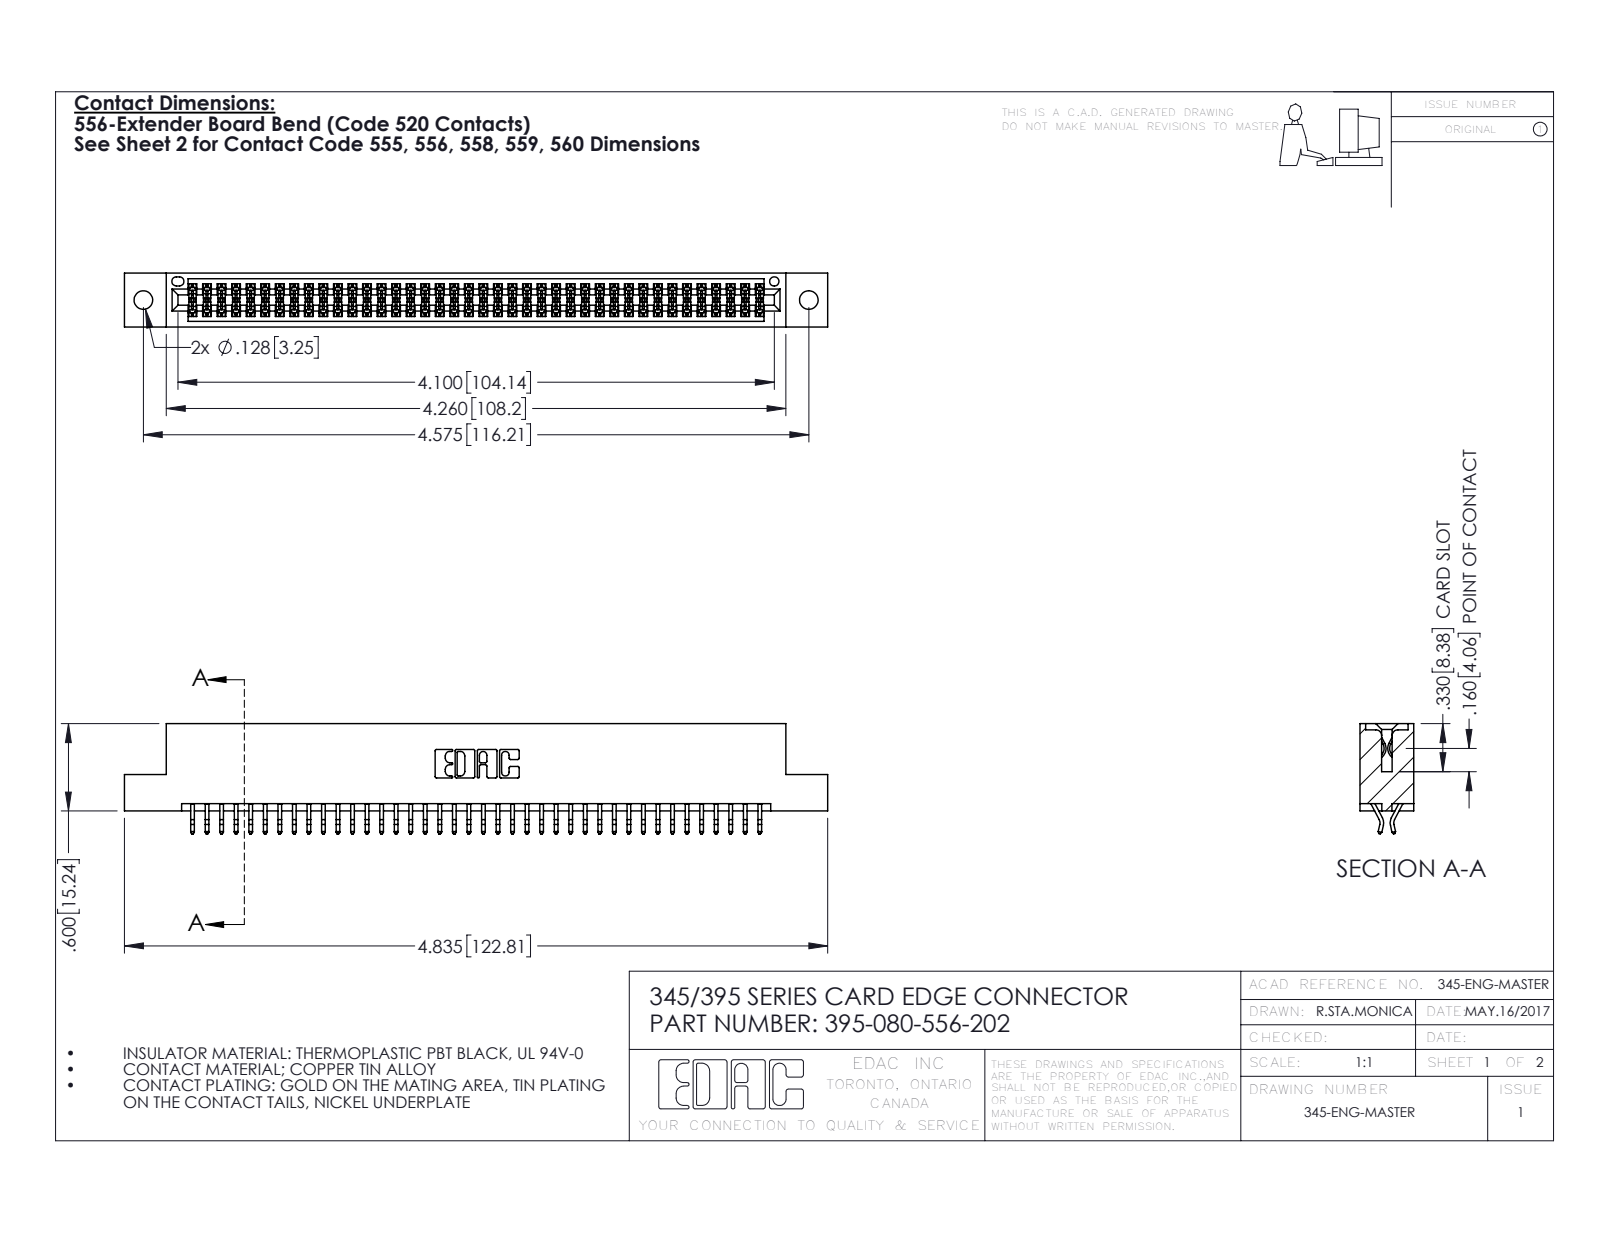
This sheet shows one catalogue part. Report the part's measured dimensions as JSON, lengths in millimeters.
{"part_name": "395-080-556-202; 345-292-001_556 Tail; 345 Part_Flush Mounting Lugs - 0.128 Dia", "step_written_by": "SolidWorks 2016 (CONFIG_CONTROL_DESIGN)", "units": "millimeters", "bodies": {"solids": 81, "faces": 4606, "planar": 3040, "cylindrical": 1566, "other": 0}, "overall_size": [122.8, 19.2, 9.4], "volume_mm3": 11900, "surface_area_mm2": 17170, "round_holes": [[3.3, 2], [1.6, 1]], "partial_cylinders_radius": [[0.2, 120], [0.3, 22], [0.2, 6], [0.8, 6], [0.7, 3], [0.3, 2], [0.4, 2], [0.5, 2]], "face_to_face_distances": [7.6, 1.8, 5.1, 9.4, 0.6, 2.5, 6.9, 5.7, 4.4, 3.8], "hole_center_spacings": [6.9, 110.2, 116.2]}
